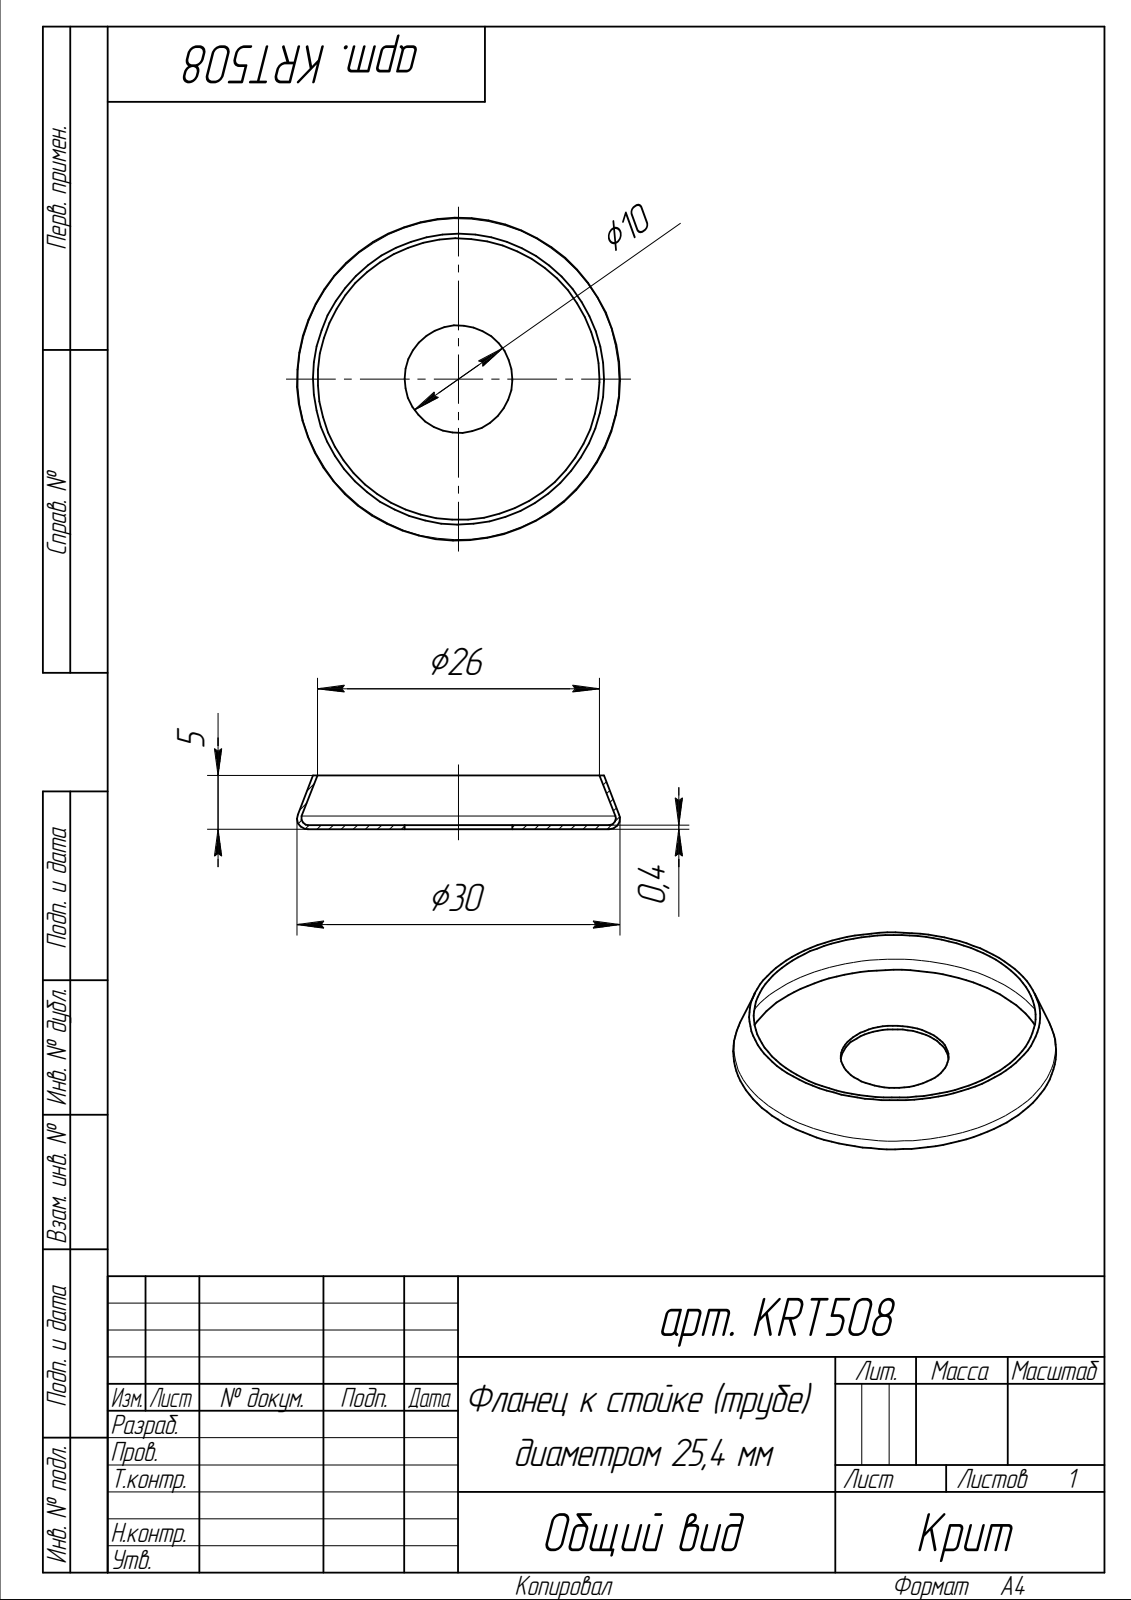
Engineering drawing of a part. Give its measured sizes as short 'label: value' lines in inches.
name: арт. KRT508
written by: SolidWorks 2014 (AUTOMOTIVE_DESIGN)
unit: in
bodies: 1 solid, 13 faces (3 planar, 2 cylindrical, 8 other)
size: 1.18 × 1.18 × 0.197
volume: 0.025 in³; area: 3.264 in²
holes: 1× ⌀0.394
face distances: 0.016, 0.197, 0.181
